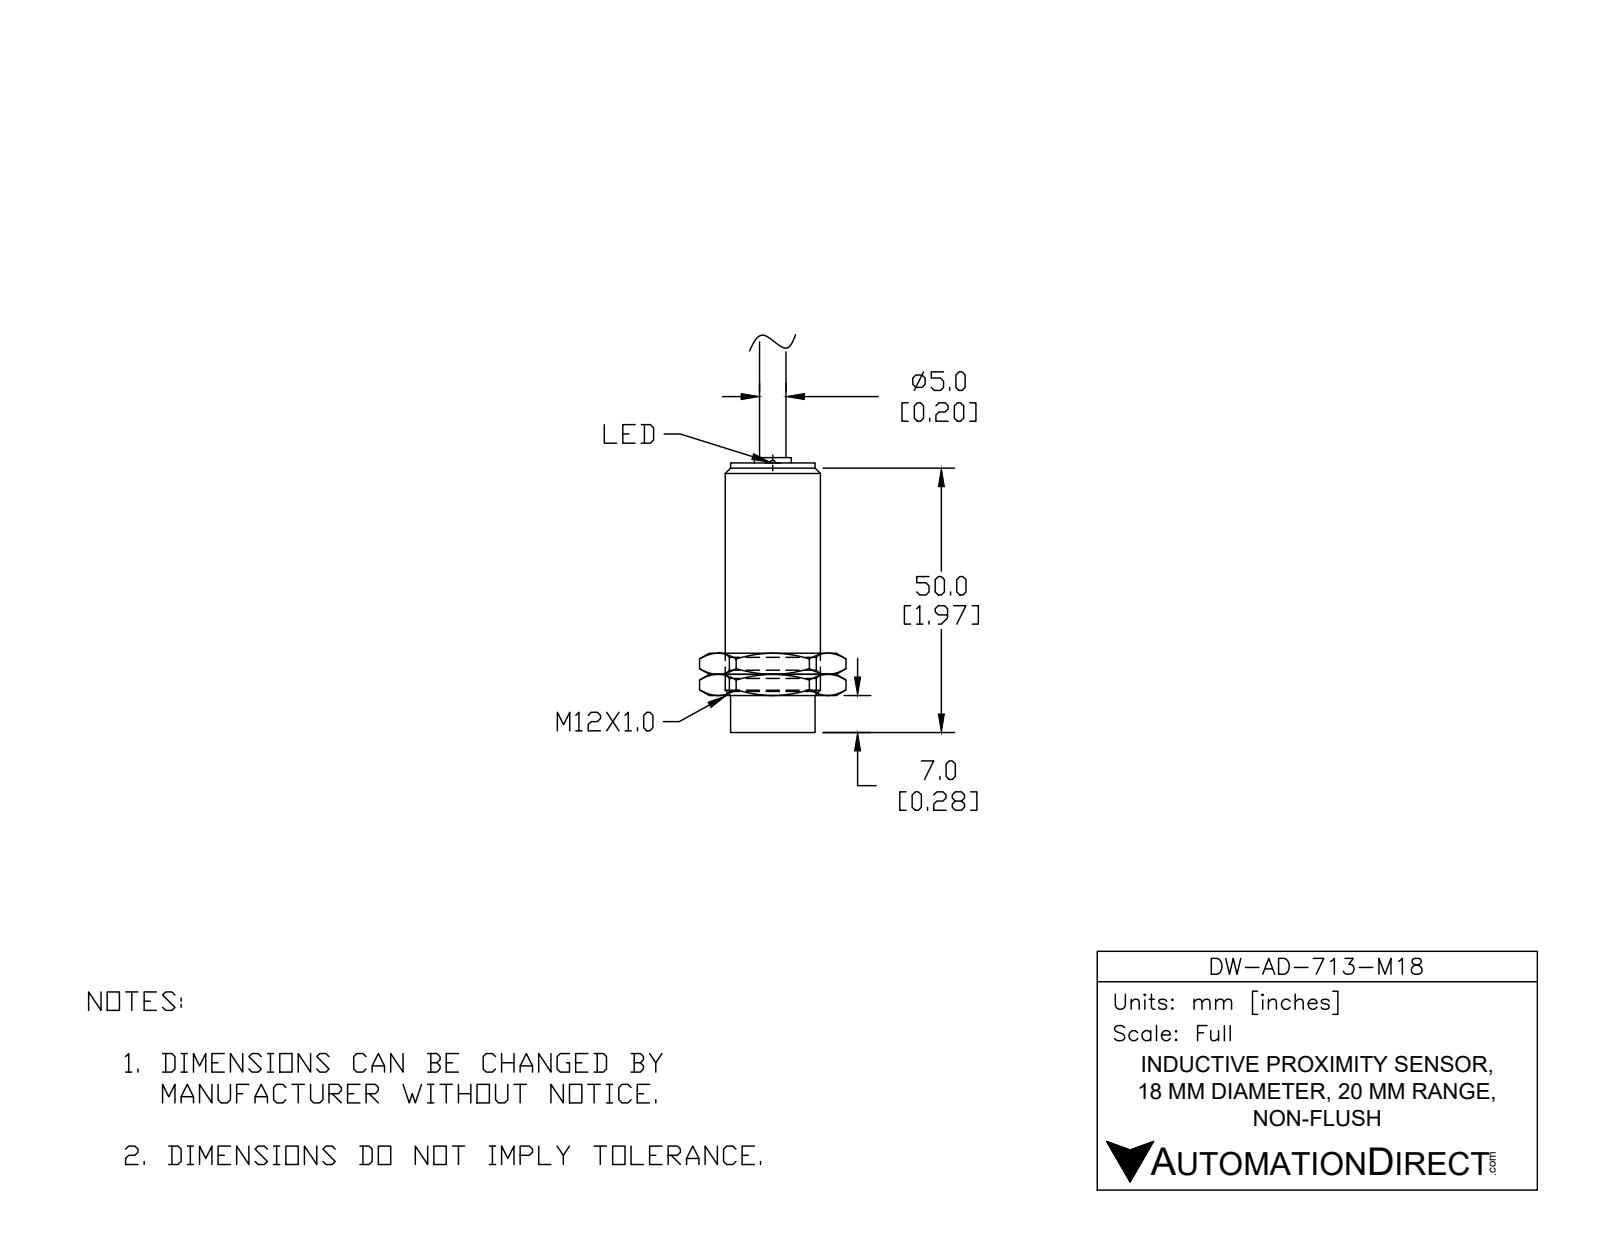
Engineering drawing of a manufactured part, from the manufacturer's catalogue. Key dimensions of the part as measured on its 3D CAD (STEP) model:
Part name (STEP PRODUCT): DW-AD-713-M18
STEP written by: SolidWorks 2017 (AUTOMOTIVE_DESIGN)
Units: inches
Bodies: 2 solids, 37 faces (18 planar, 7 cylindrical, 12 other)
Overall size (bounding box): 3.016 × 0.709 × 0.709
Volume: 0.81 in³ · Surface area: 5.918 in²
Round bosses / shafts (diameter × count): ⌀0.709 ×1, ⌀0.646 ×1, ⌀0.413 ×1, ⌀0.268 ×1, ⌀0.197 ×1, ⌀0.118 ×1
Main face-to-face distances: 2.008, 0.031, 2.087, 0.079, 2.039, 0.047, 1.89, 0.118, 0.15, 0.197
